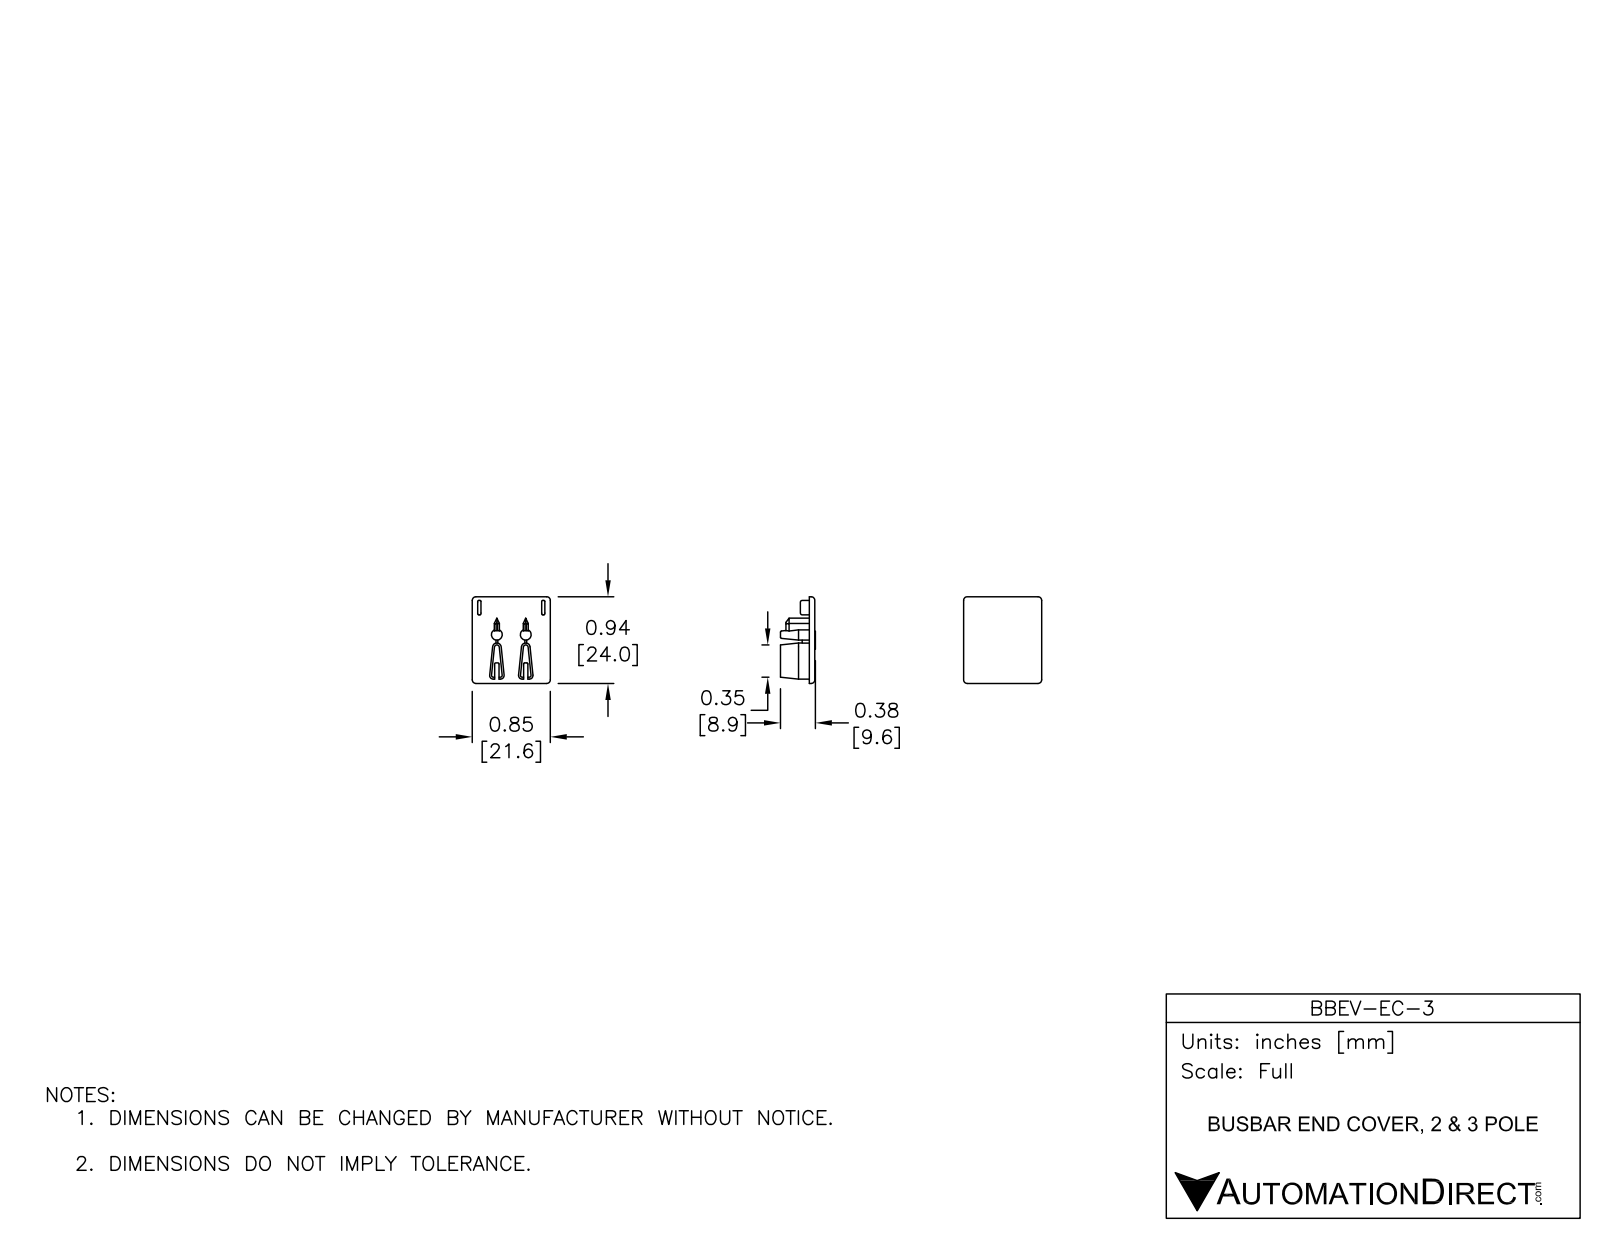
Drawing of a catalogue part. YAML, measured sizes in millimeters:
part_name: "BBEV-EC-3"
step_written_by: "SolidWorks 2014 (AUTOMOTIVE_DESIGN)"
units: millimeters
bodies: {solids: 1, faces: 56, planar: 29, cylindrical: 23, other: 4}
overall_size: [24, 21.6, 9.65]
volume: 1254
surface_area: 1531
partial_cylinders:
  - {radius: 1, count: 12}
  - {radius: 1.2, count: 2}
  - {radius: 2.15, count: 2}
  - {radius: 2.9, count: 2}
face_to_face_distances: [1.5, 7.96, 8, 9.5, 1.65, 9.65, 21.6, 1.2, 22.8, 24]
